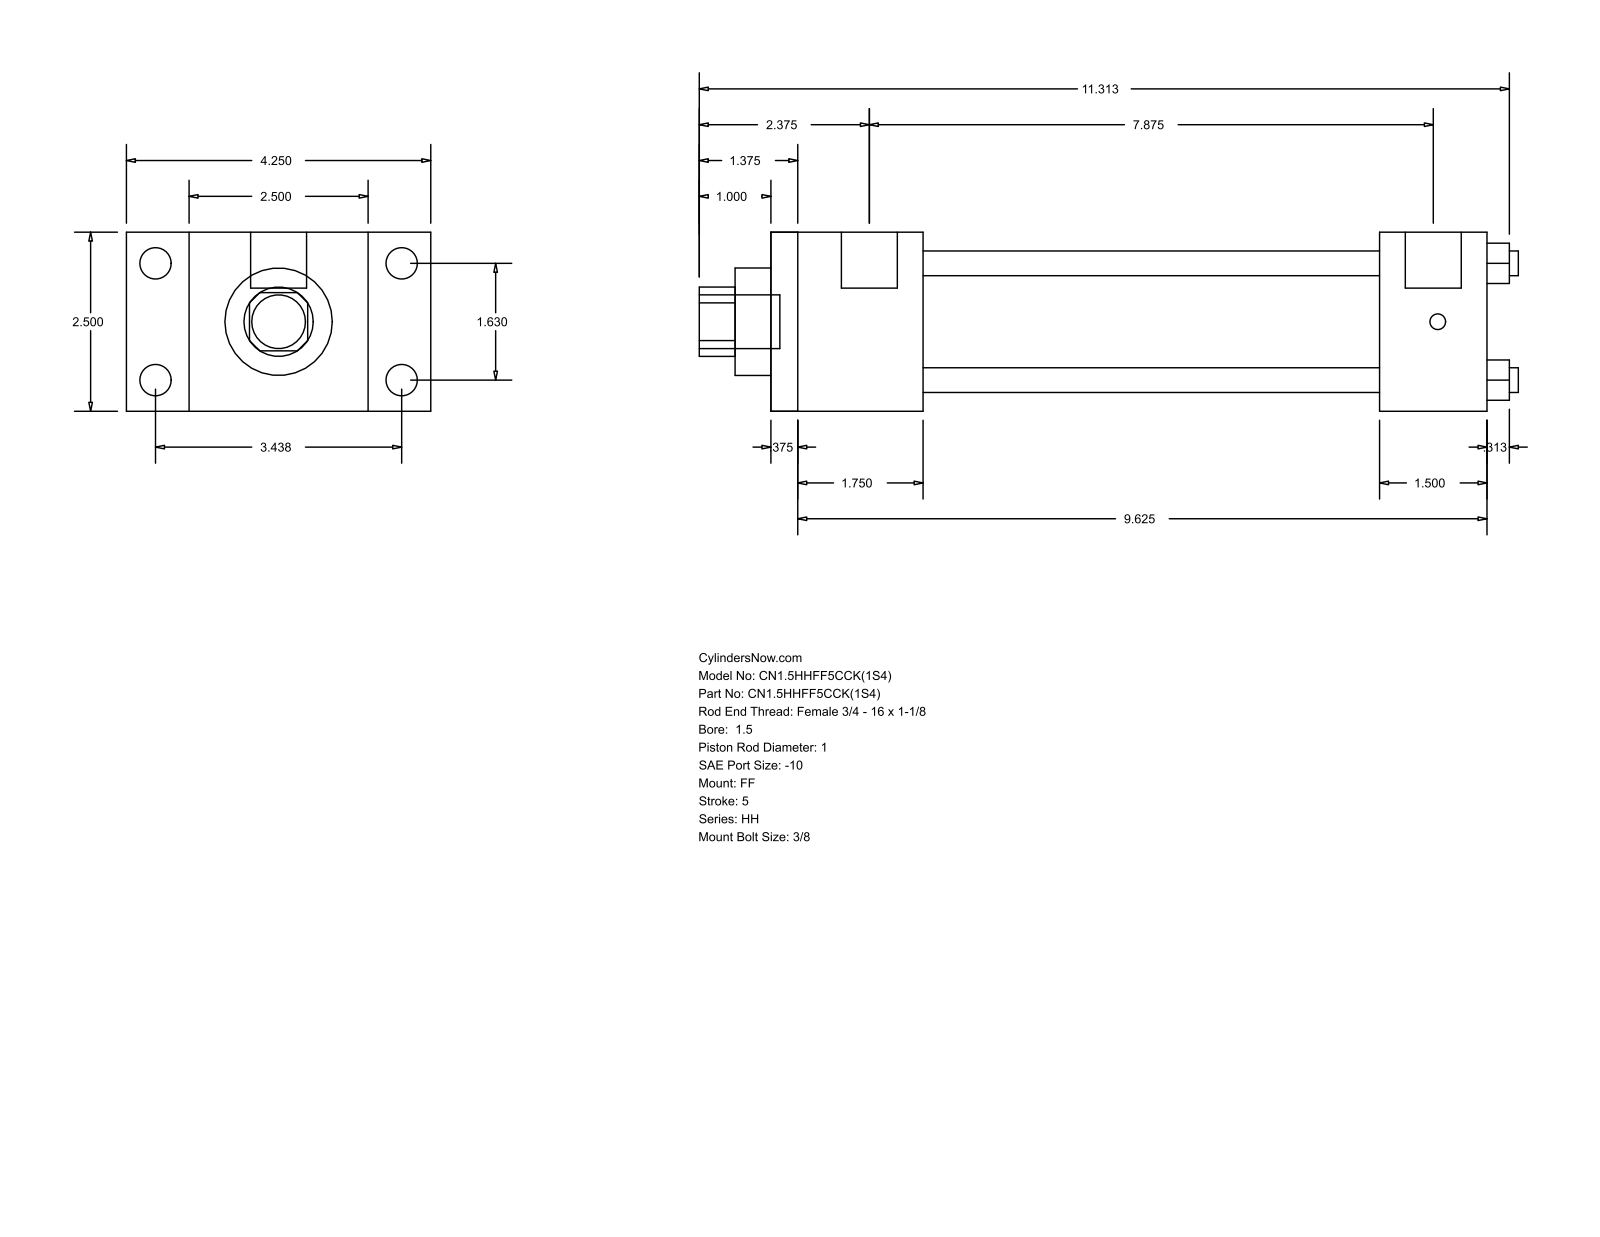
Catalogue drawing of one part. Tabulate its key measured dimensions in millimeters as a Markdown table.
| quantity | value |
| --- | --- |
| part name | HH_FF__0150_1 |
| STEP written by | GSSL Pune (CONFIG_CONTROL_DESIGN) |
| units | millimeters |
| bodies | 0 solids, 92 faces (64 planar, 28 cylindrical, 0 other) |
| overall size | 290.51 × 107.95 × 63.5 |
| round holes (diameter × count) | 8.76 × 4, 25.4 × 1, 38.1 × 1, 44.45 × 1 |
| round bosses / shafts (diameter × count) | 11.13 × 4, 5.56 × 4, 19.84 × 2, 19.05 × 1 |
| partial cylindrical surfaces (radius × count) | 12.29 × 1 |
| main face-to-face distances | 63.5, 254, 9.52, 244.48, 53.98, 44.46, 200.02, 215.9, 206.38, 161.92 |
| hole center spacings | 29.27, 41.4, 58.55 |
